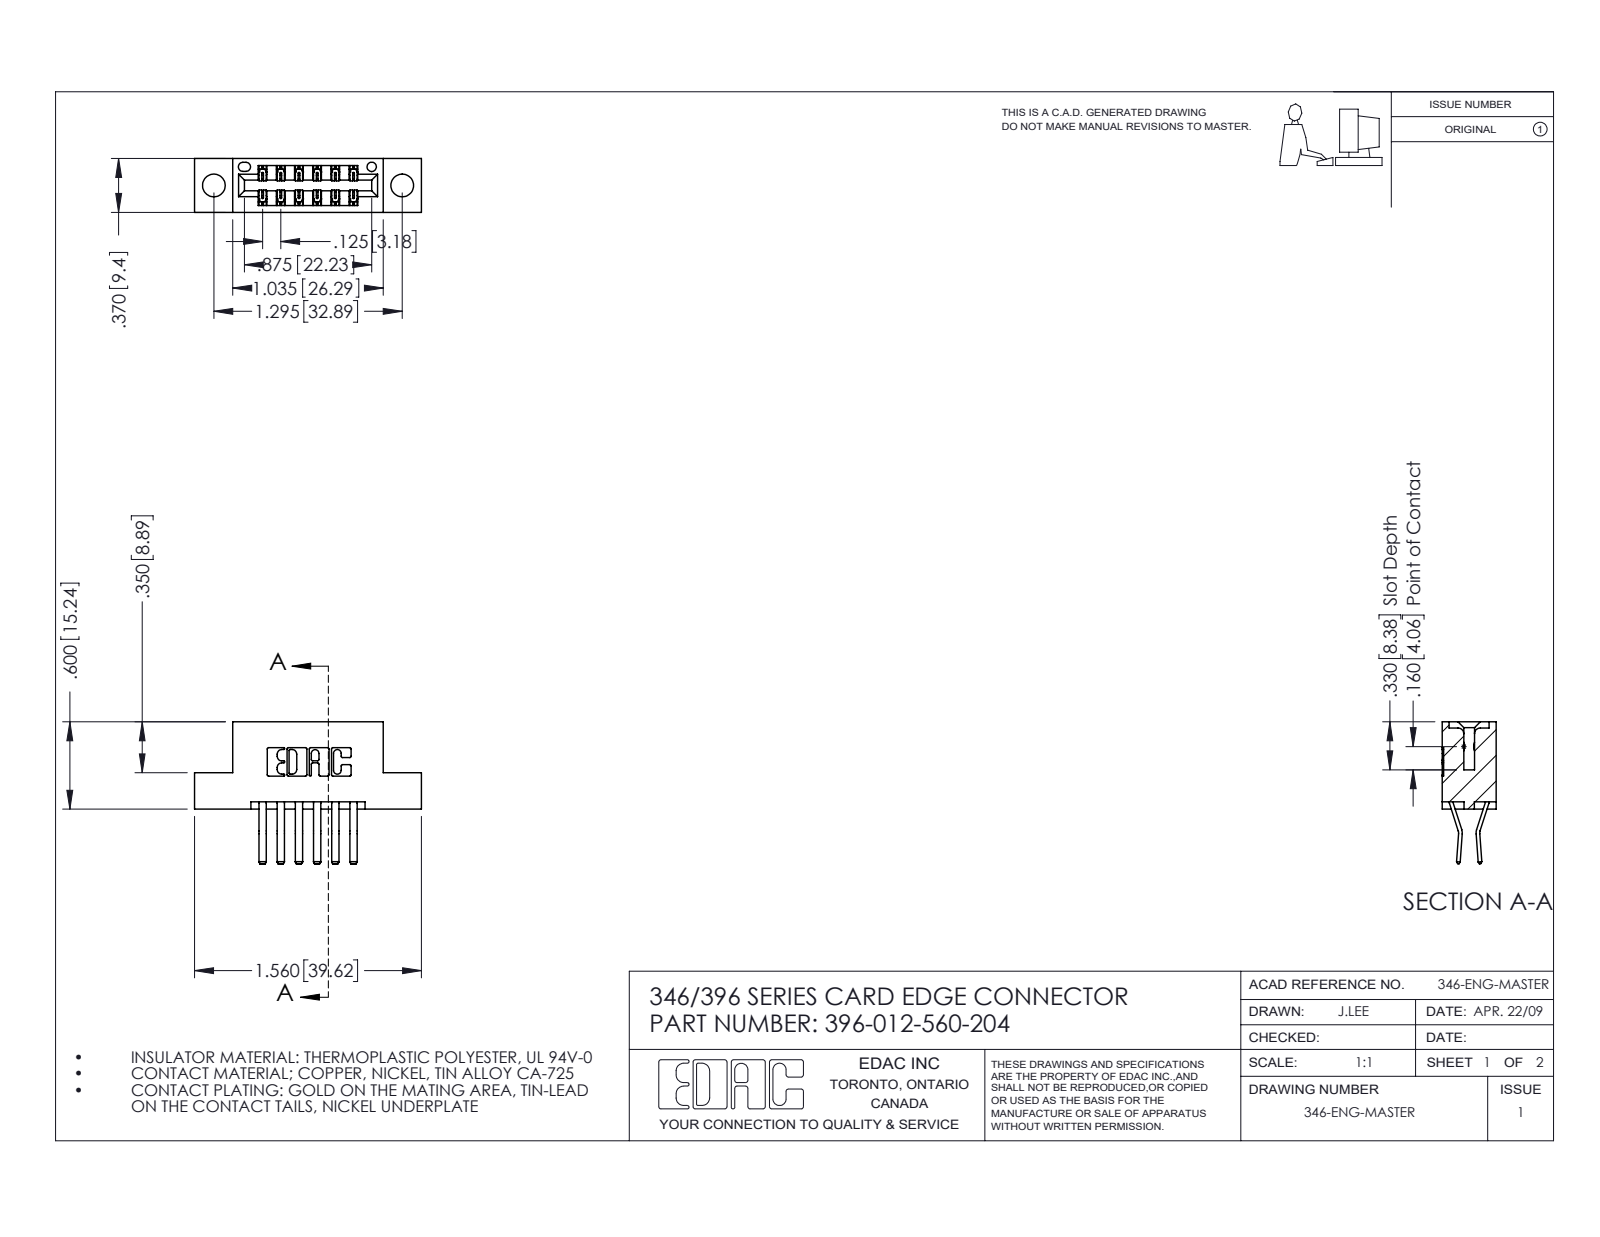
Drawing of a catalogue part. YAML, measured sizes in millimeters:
part_name: "346 Part_Flush Mounting Lugs - 0.156 Dia-TH; 345-292-001_560 Tail; 396-012-560-204"
step_written_by: "SolidWorks 2016 (CONFIG_CONTROL_DESIGN)"
units: millimeters
bodies: {solids: 13, faces: 770, planar: 496, cylindrical: 274, other: 0}
overall_size: [39.6, 24.8, 9.4]
volume: 3570
surface_area: 4372
round_holes:
  - {diameter: 4, count: 2}
  - {diameter: 1.6, count: 1}
partial_cylinders:
  - {radius: 0.3, count: 22}
  - {radius: 0.2, count: 18}
  - {radius: 0.2, count: 6}
  - {radius: 0.8, count: 6}
  - {radius: 0.7, count: 3}
  - {radius: 0.3, count: 2}
  - {radius: 0.4, count: 2}
  - {radius: 0.6, count: 2}
face_to_face_distances: [6.4, 9.4, 1.2, 8.2, 0.6, 3.2, 3.8, 5.6, 2.5, 4.4]
hole_center_spacings: [6.2, 27.7, 32.9]
